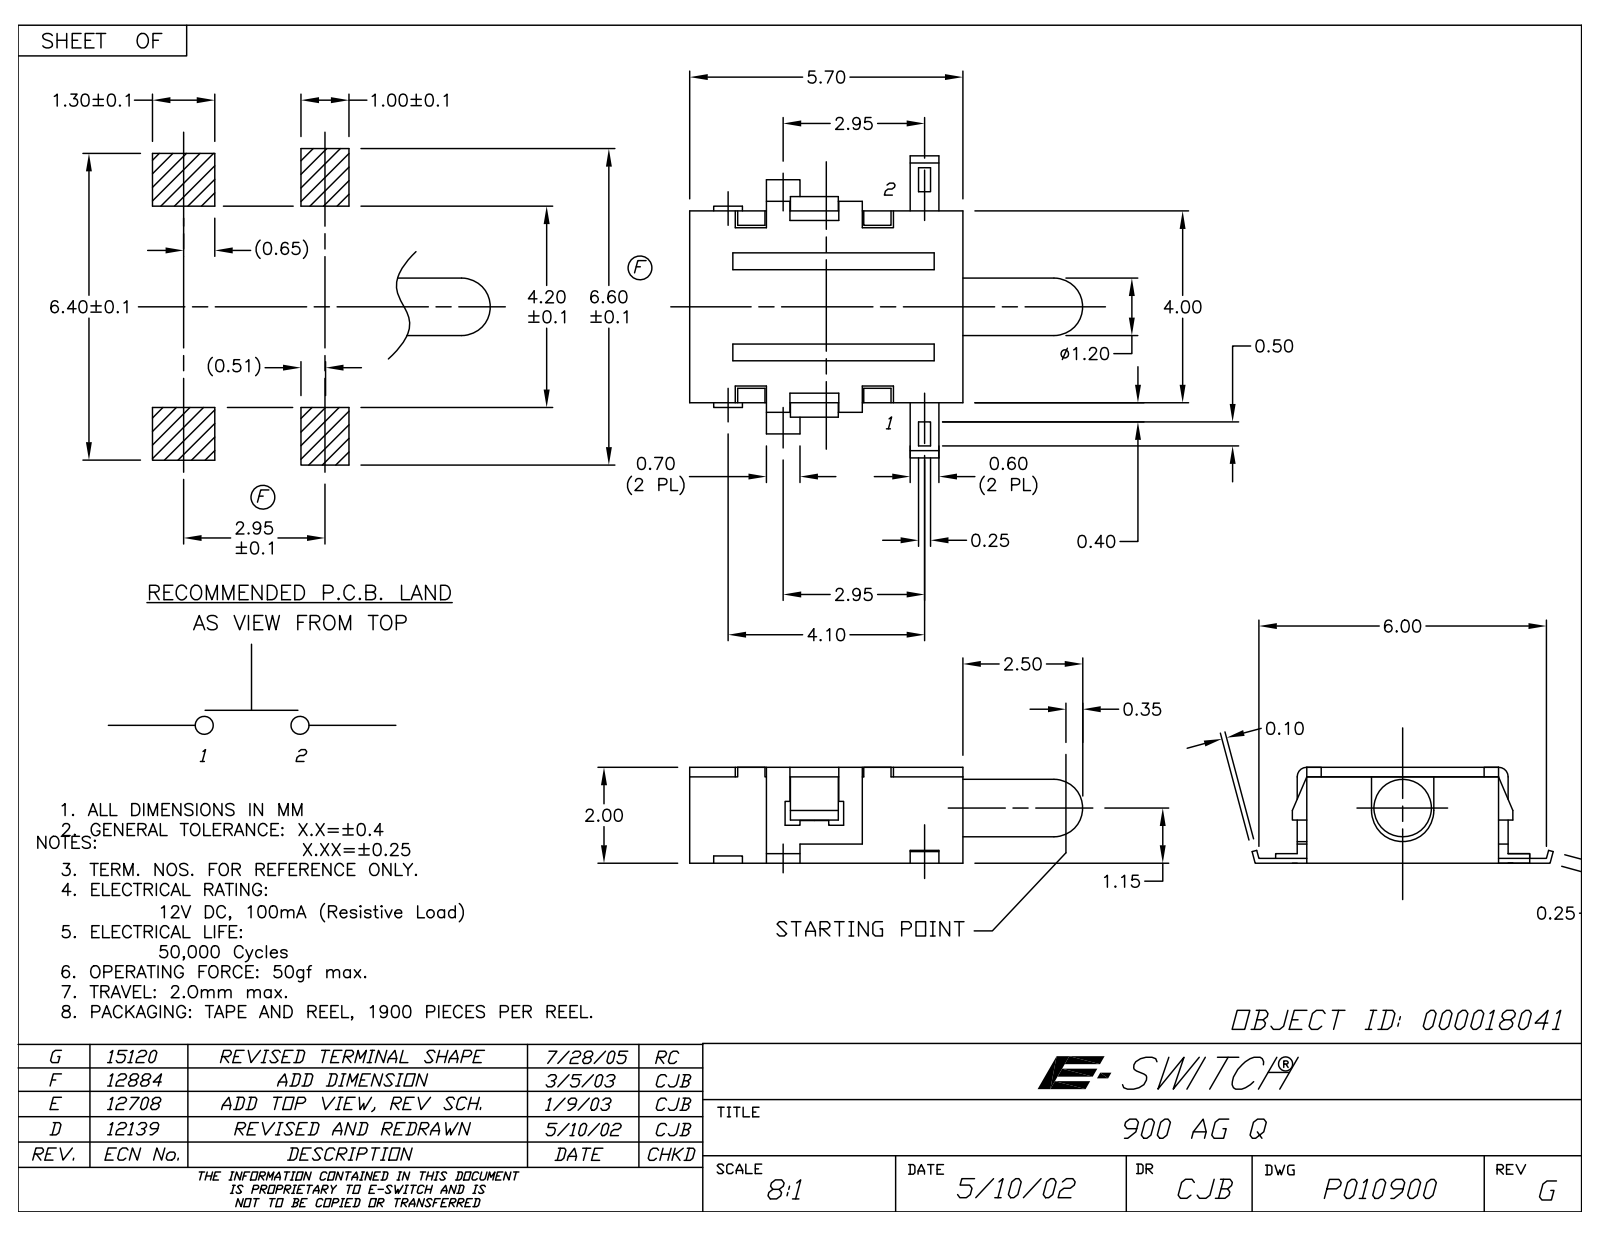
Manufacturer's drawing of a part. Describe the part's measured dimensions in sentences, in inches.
Its 3-D file was written by "Autodesk Inventor 2012 (CONFIG_CONTROL_DESIGN)". It is 1 solid with 148 faces: 123 planar, 20 cylindrical and 5 other. Overall it measures 0.323 by 0.256 by 0.079 inches. Its volume is 0.002 cubic inches and its surface area 0.285 square inches. Round holes: 4 of diameter 0.01. Round bosses or shafts: 1 of diameter 0.047. Partial cylindrical surfaces (rounded edges, fillets, slot ends): 8 of radius 0.006, 4 of radius 0.008, 1 of radius 0.025. The main face-to-face distances are 0.079, 0.059, 0.067, 0.014, 0.071, 0.051, 0.055, 0.144, 0.063, 0.02. The hole center spacings are 0.079, 0.138, 0.159.
